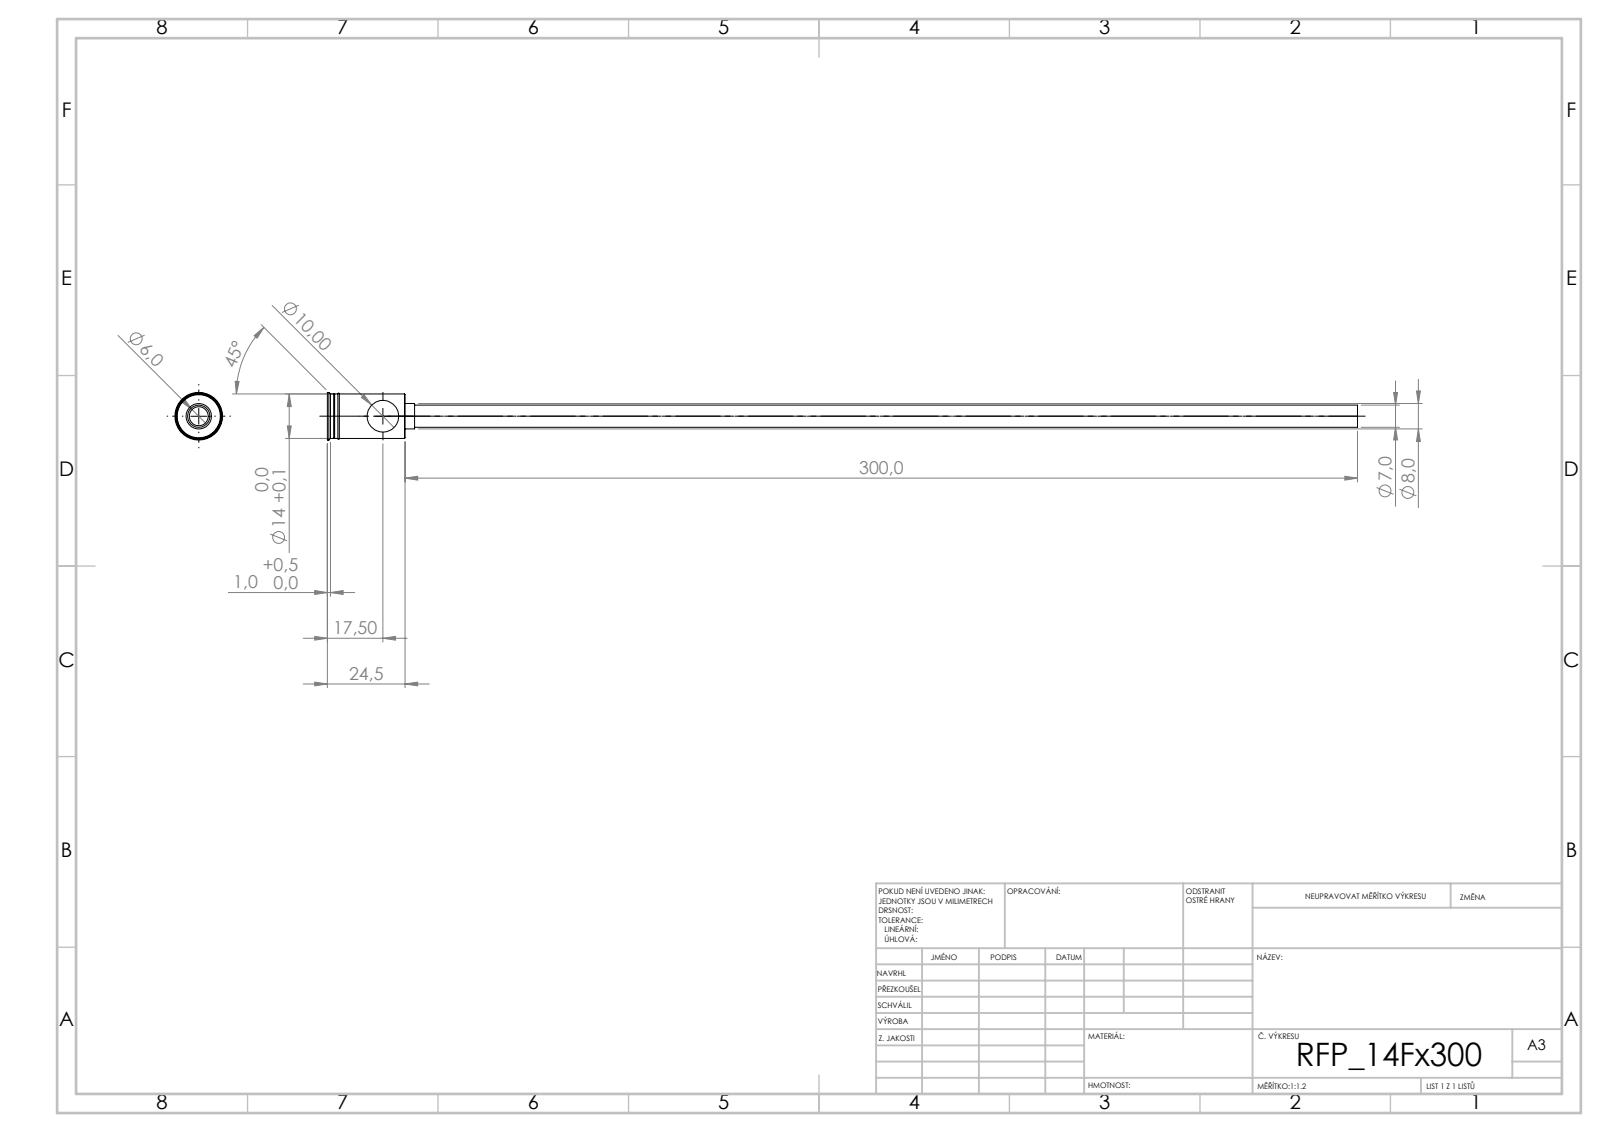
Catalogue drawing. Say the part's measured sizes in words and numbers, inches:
Its 3-D file was written by "SolidWorks 2019 (CONFIG_CONTROL_DESIGN)". It is 1 solid with 44 faces: 20 planar, 16 cylindrical and 8 other. Overall it measures 12.776 by 0.591 by 0.591 inches. Its volume is 0.345 cubic inches and its surface area 21.65 square inches. Round holes: 1 of diameter 0.236, 1 of diameter 0.394. Round bosses or shafts: 1 of diameter 0.591, 1 of diameter 0.551, 1 of diameter 0.315, 1 of diameter 0.276. The main face-to-face distances are 0.965, 0.886, 0.079, 0.37, 0.874, 0.091, 0.118, 0.992, 1.004, 1.083.
